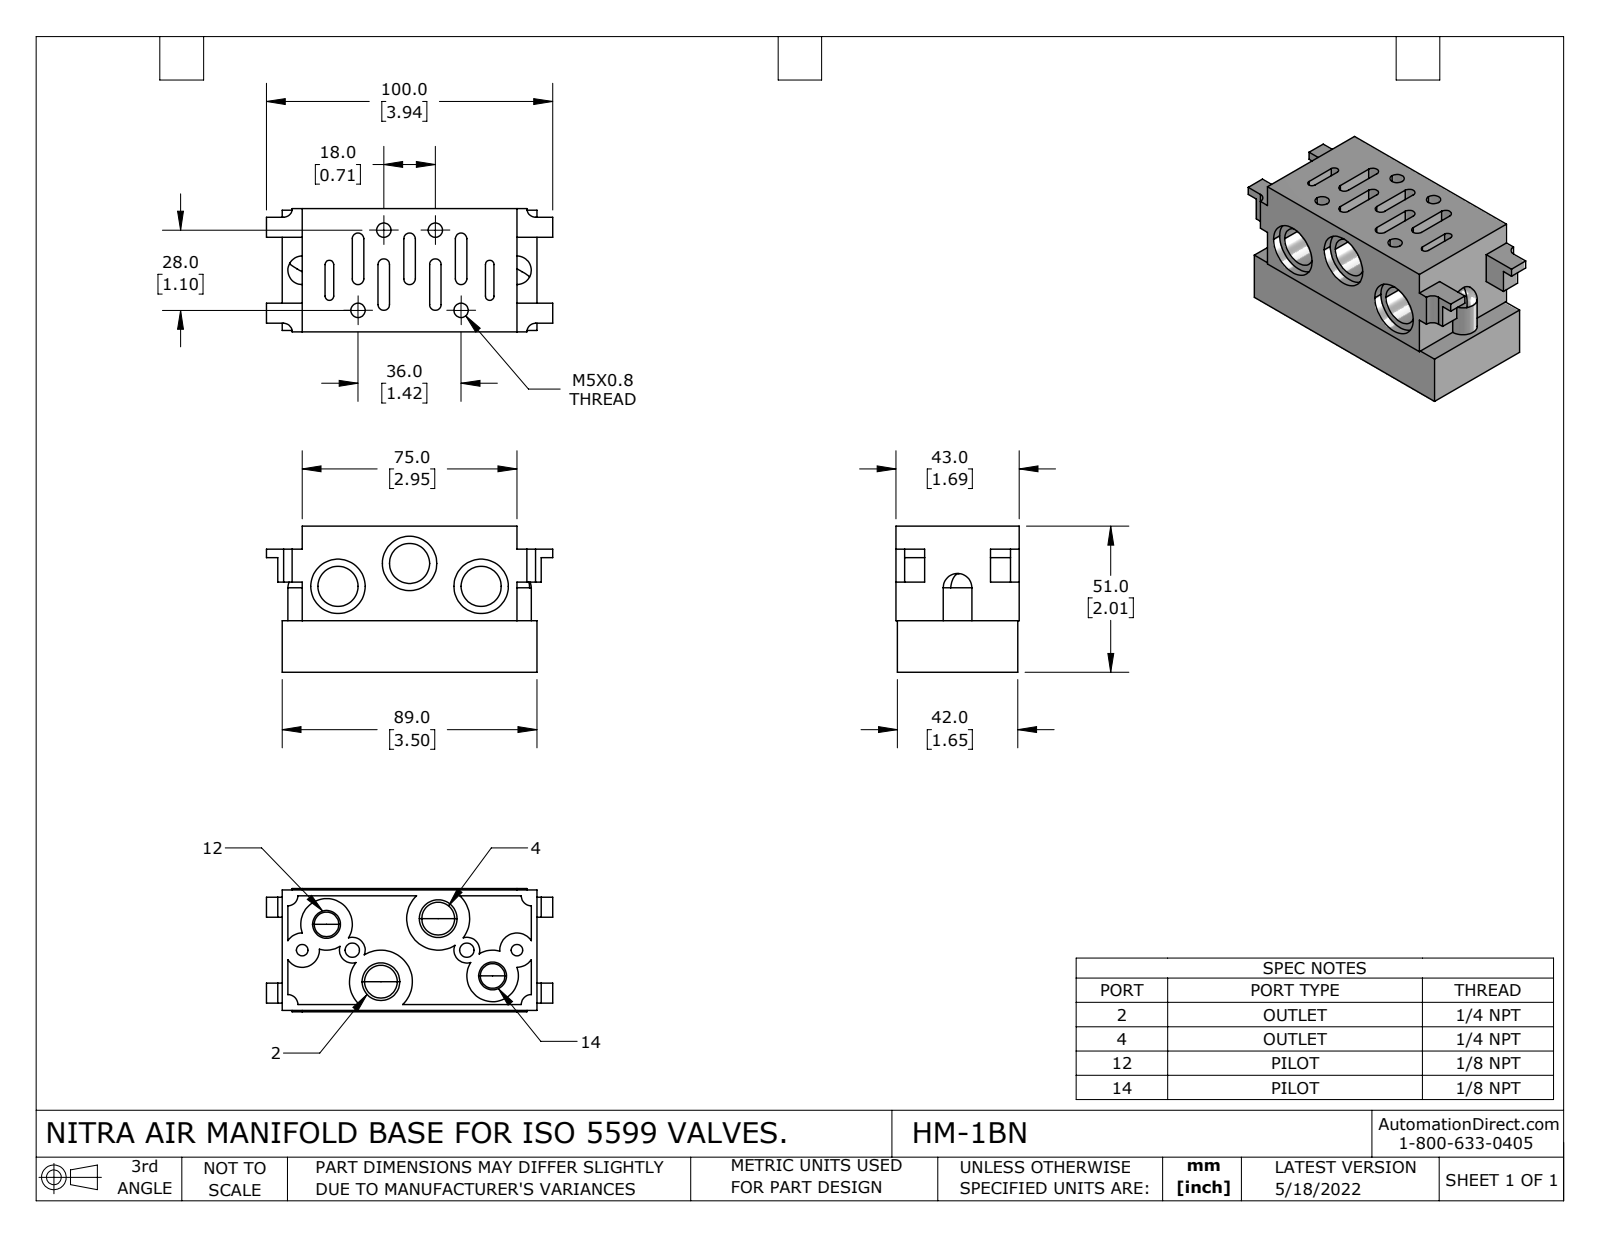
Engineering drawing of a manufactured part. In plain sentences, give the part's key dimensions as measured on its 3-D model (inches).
The part is named "HM-1BN". Its 3-D file was written by "SolidWorks 2021 (CONFIG_CONTROL_DESIGN)". It is 1 solid with 181 faces: 85 planar, 76 cylindrical and 20 other. Overall it measures 3.937 by 2.008 by 1.693 inches. Its volume is 7.605 cubic inches and its surface area 58.9 square inches. Round holes: 6 of diameter 0.197, 3 of diameter 0.551, 3 of diameter 0.748, 2 of diameter 0.157, 2 of diameter 0.337, 2 of diameter 0.451. Partial cylindrical surfaces (rounded edges, fillets, slot ends): 10 of radius 0.079, 4 of radius 0.059, 4 of radius 0.118, 4 of radius 0.138, 2 of radius 0.177, 2 of radius 0.197, 2 of radius 0.236, 2 of radius 0.354. The main face-to-face distances are 0.02, 1.673, 1.575, 0.079, 0.098, 1.693, 1.594, 1.457, 0.276, 0.551. The hole center spacings are 1.033, 0.487, 0.501, 0.557, 0.585, 0.689, 0.701, 0.945.
